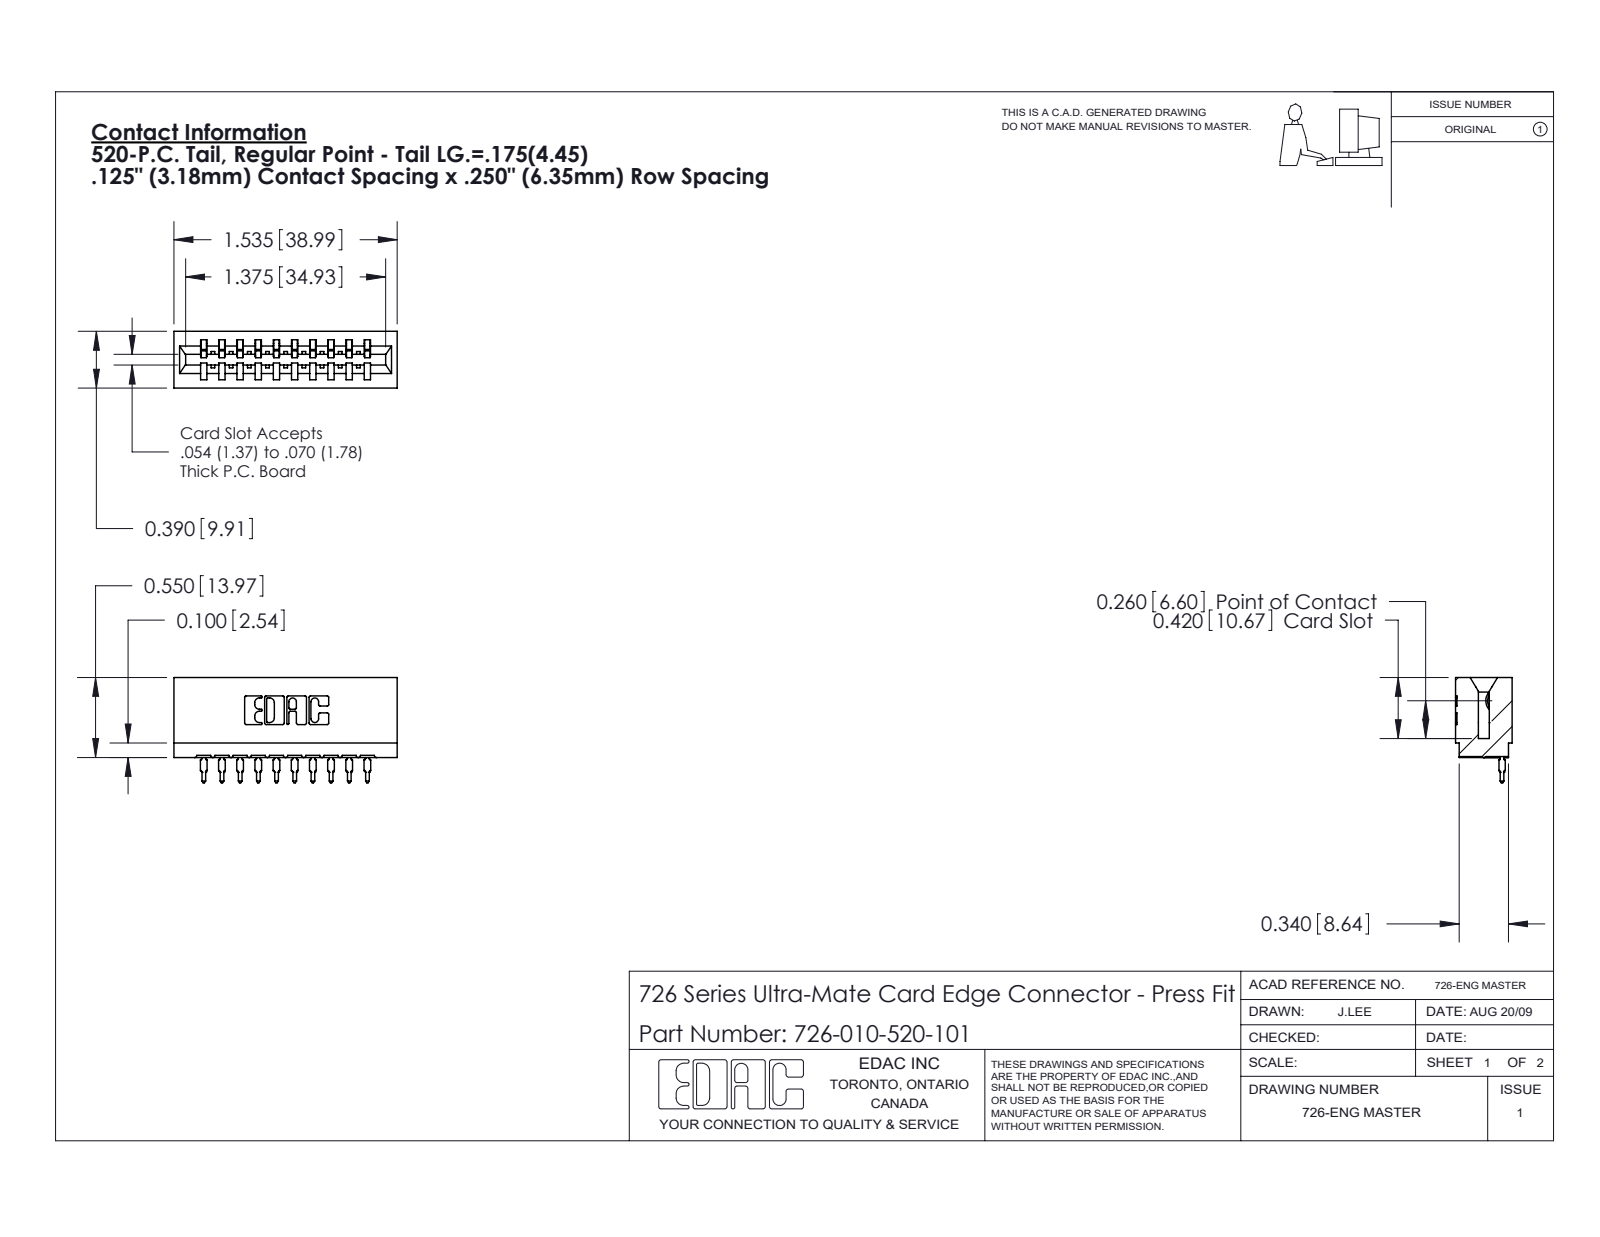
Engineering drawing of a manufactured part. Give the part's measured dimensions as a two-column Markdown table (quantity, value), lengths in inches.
| quantity | value |
| --- | --- |
| part name | 726-010-520-101; 726 Part_.515 Slot Depth - 01; 746-292-001_520 |
| STEP written by | SolidWorks 2020 (CONFIG_CONTROL_DESIGN) |
| units | inches |
| bodies | 11 solids, 1177 faces (685 planar, 232 cylindrical, 260 other) |
| overall size | 1.535 × 0.724 × 0.39 |
| volume | 0.223 in³ |
| surface area | 7.795 in² |
| partial cylindrical surfaces (radius × count) | 0.01 × 22, 0.021 × 20, 0.015 × 11, 0.007 × 6, 0.031 × 6, 0.005 × 4, 0.011 × 4, 0.026 × 3 |
| main face-to-face distances | 0.25, 0.125, 0.333, 0.042, 0.75, 0.5, 0.057, 0.39, 0.292, 0.375 |
